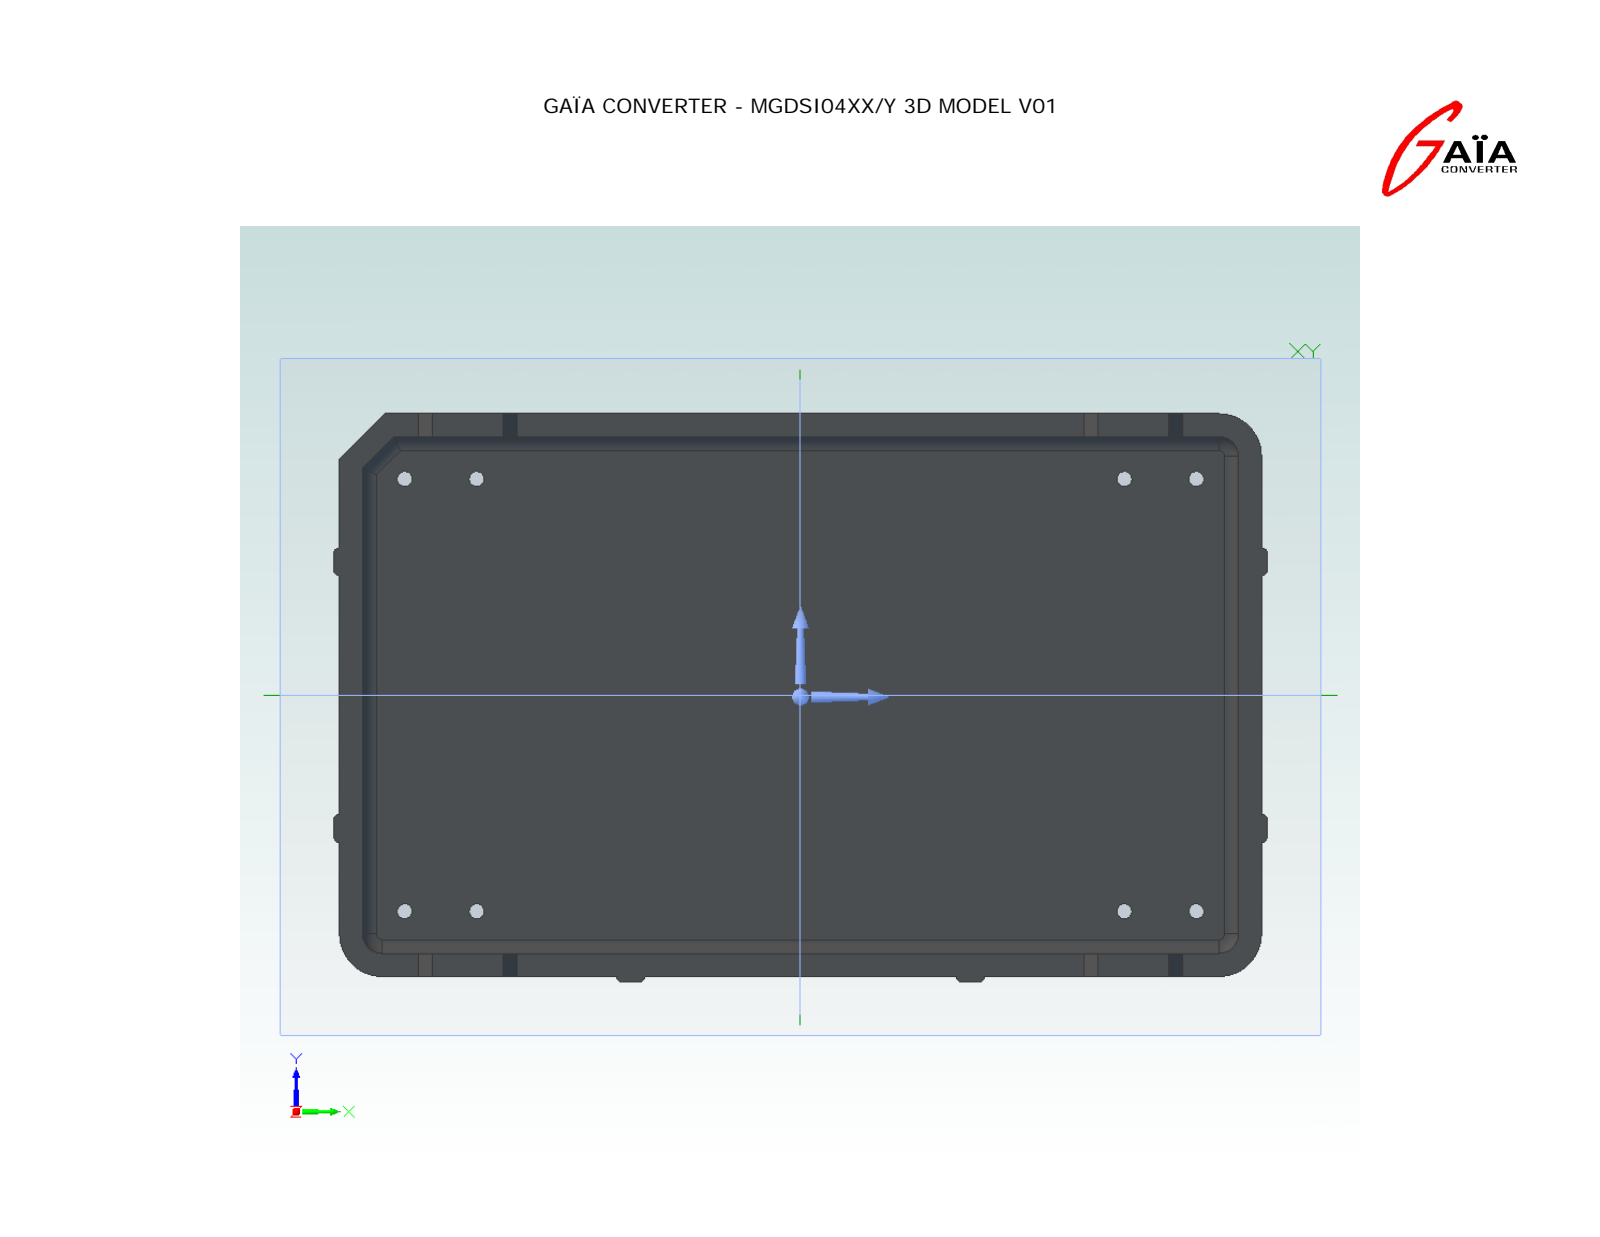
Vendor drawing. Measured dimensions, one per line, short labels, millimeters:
name: MGDSI04XX_Y_V01_BOOLEAN_FOR_STEP
written by: Alibre (AUTOMOTIVE_DESIGN)
unit: mm
bodies: 1 solid, 453 faces (304 planar, 76 cylindrical, 73 other)
size: 32.94 × 20.05 × 13.51
volume: 1 076 mm³; area: 3 823 mm²
bosses: 8× ⌀0.53, 5× ⌀0.9, 1× ⌀2, 1× ⌀0.7, 1× ⌀0.69
rounds: 15× R0.2, 14× R1, 8× R1.5, 5× R0.49, 3× R0.45, 3× R0.7
face distances: 0.8, 6.81, 6.8, 6, 6.01, 19.04, 31.74, 18.24, 19.84, 0.81
